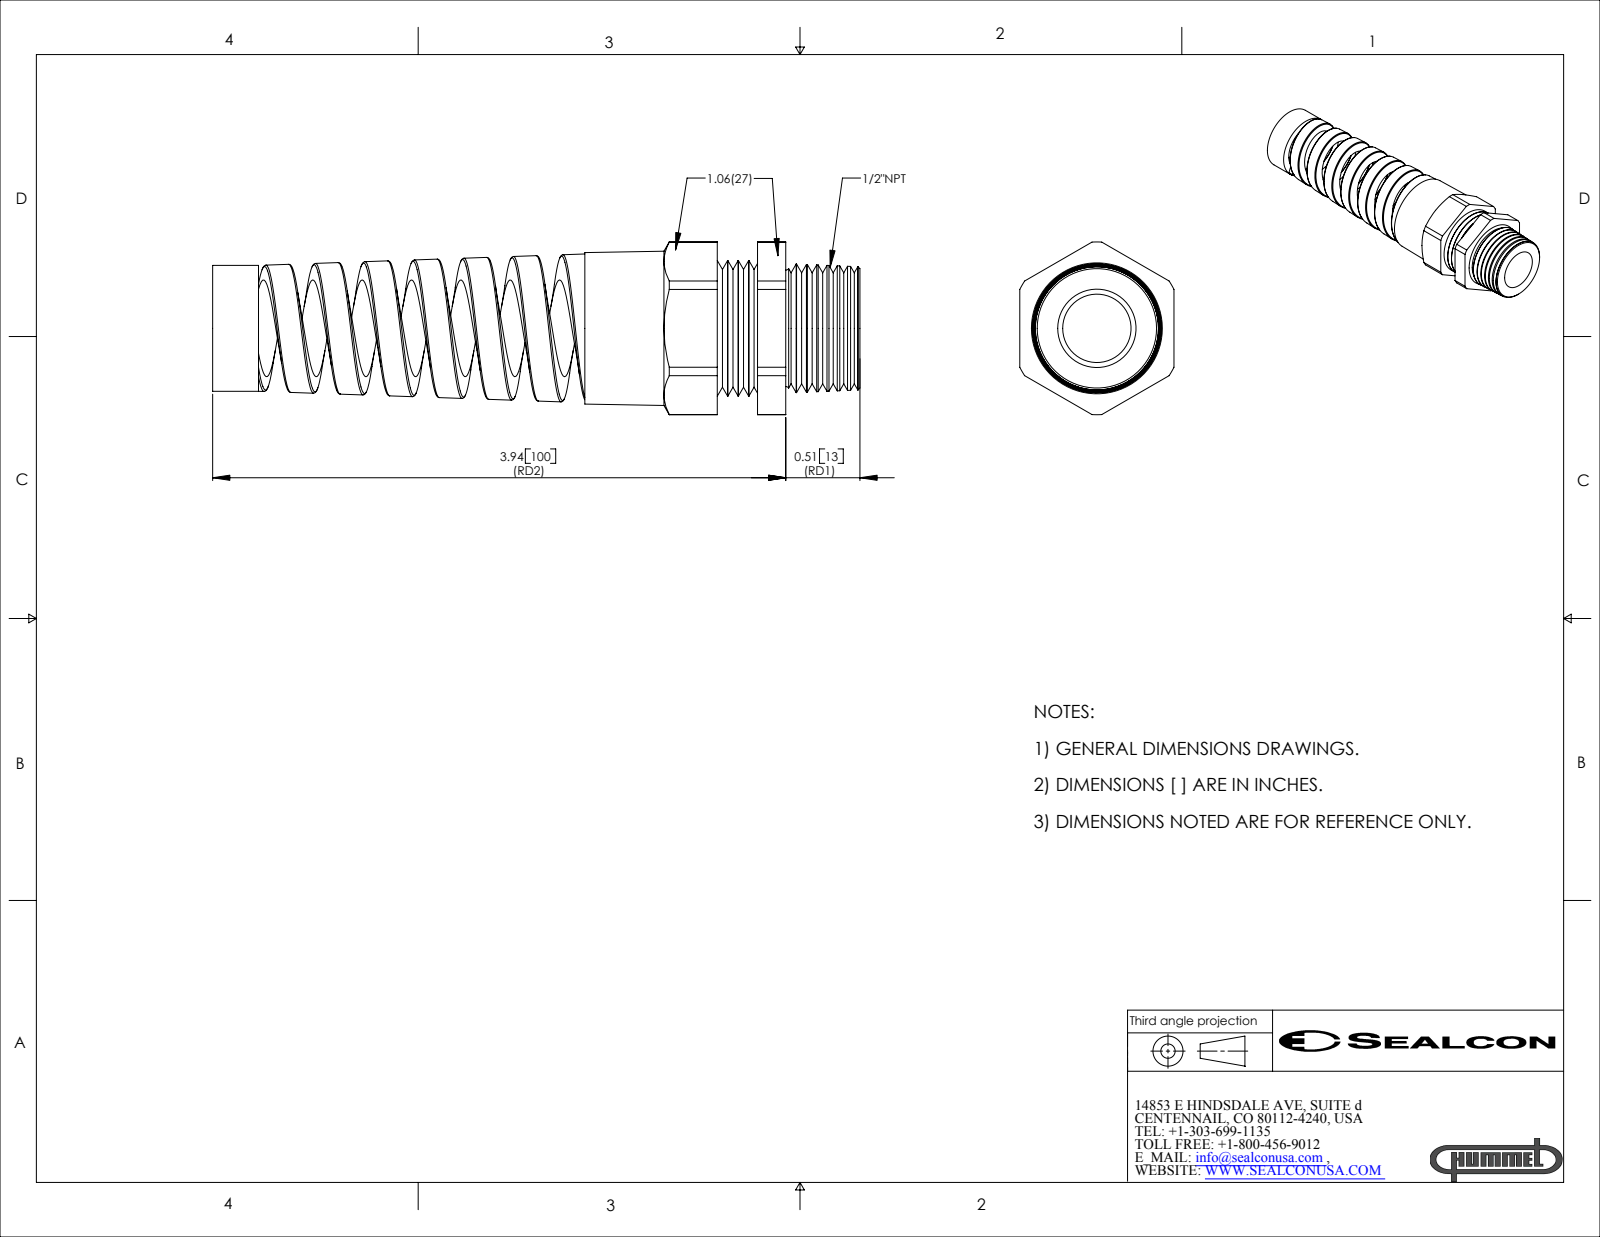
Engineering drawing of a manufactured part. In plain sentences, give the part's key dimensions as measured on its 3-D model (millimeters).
The part is named "CF16NR-GY". Its 3-D file was written by "SolidWorks 2007 (CONFIG_CONTROL_DESIGN)". It is 1 solid with 153 faces: 19 planar, 39 cylindrical and 95 other. Overall it measures 113 by 30.1 by 26.9 millimeters. Its volume is 26 140 cubic millimeters and its surface area 16 230 square millimeters. Round holes: 1 of diameter 11.9, 1 of diameter 16.9. Round bosses or shafts: 1 of diameter 23.7, 1 of diameter 22. Partial cylindrical surfaces (rounded edges, fillets, slot ends): 1 of radius 15.1. The main face-to-face distances are 26.9, 35.1, 48, 13, 23.1, 12, 24.9, 30.1, 7, 4.9.
